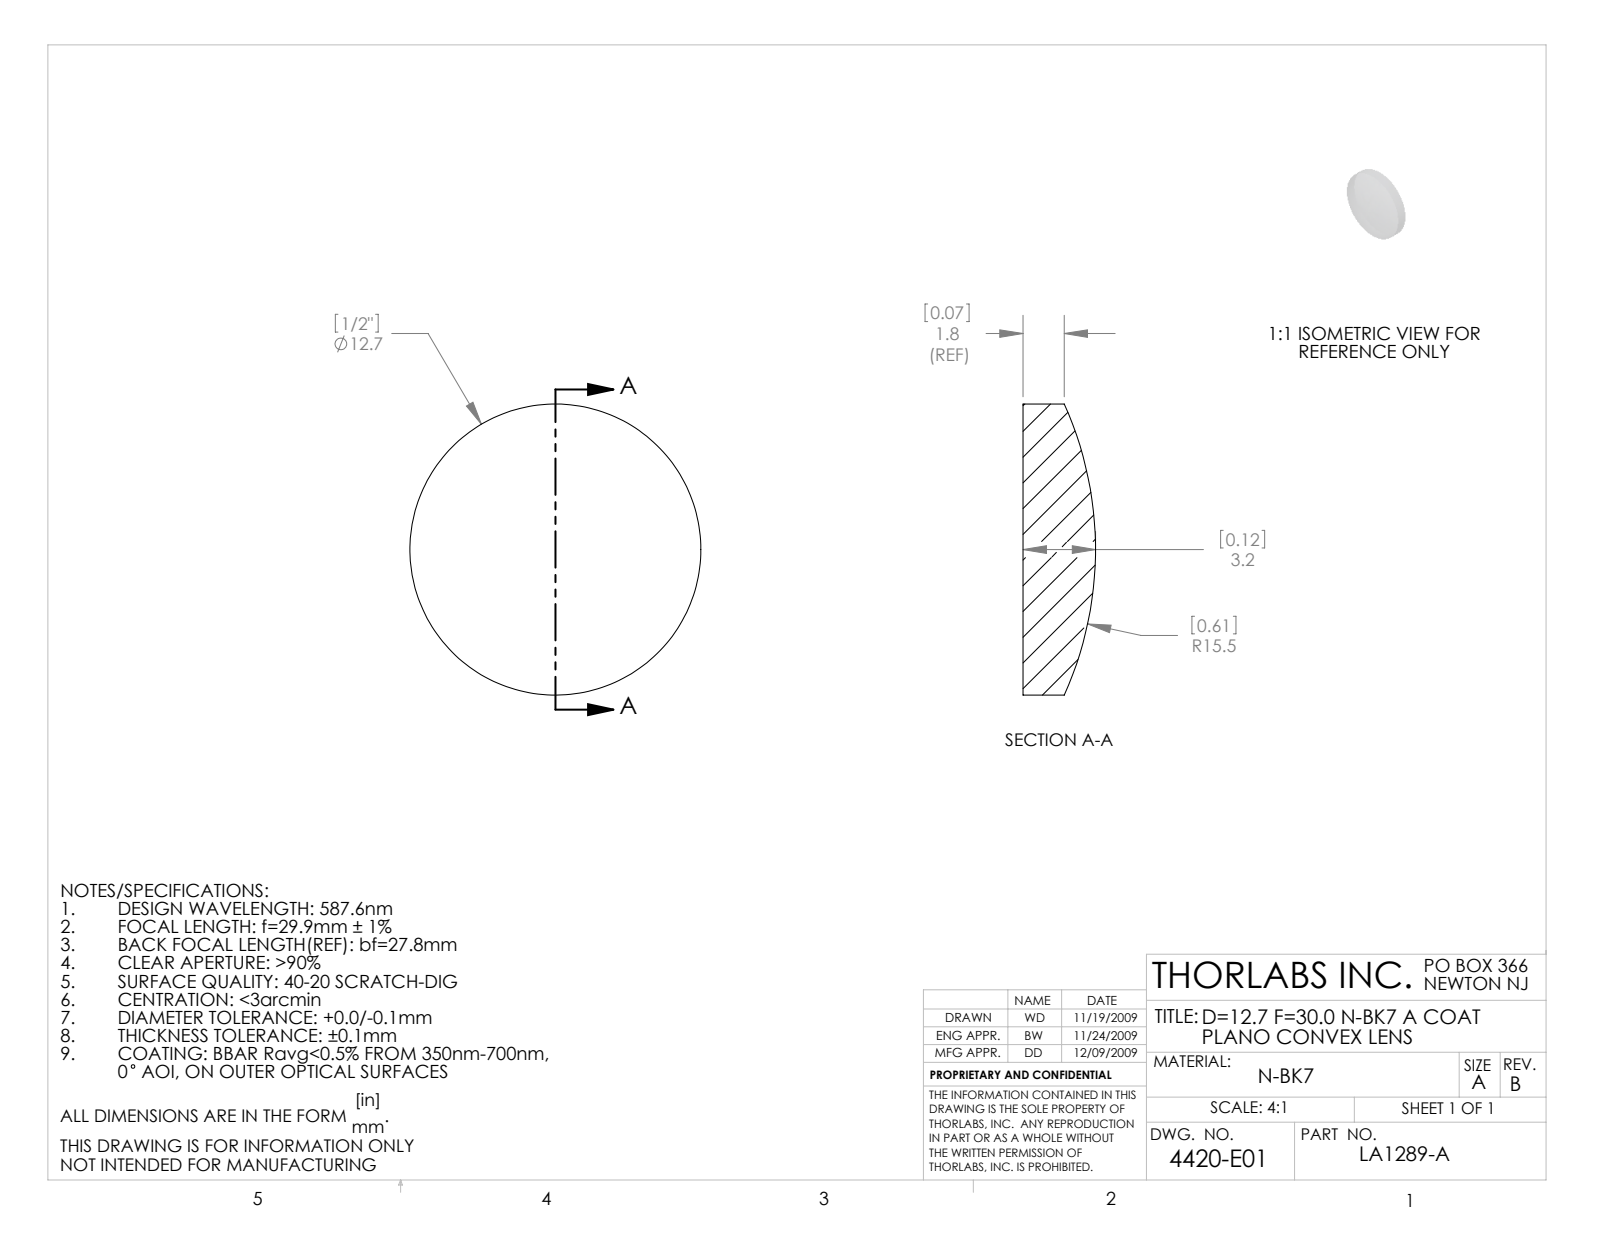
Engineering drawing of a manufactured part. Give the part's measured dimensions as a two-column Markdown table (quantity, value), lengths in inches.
| quantity | value |
| --- | --- |
| part name | 4420-E0W |
| STEP written by | SolidWorks 2009 (AUTOMOTIVE_DESIGN) |
| units | inches |
| bodies | 1 solid, 5 faces (1 planar, 2 cylindrical, 2 other) |
| overall size | 0.5 × 0.5 × 0.124 |
| volume | 0.019 in³ |
| surface area | 0.513 in² |
| round bosses / shafts (diameter × count) | 0.5 × 1 |
